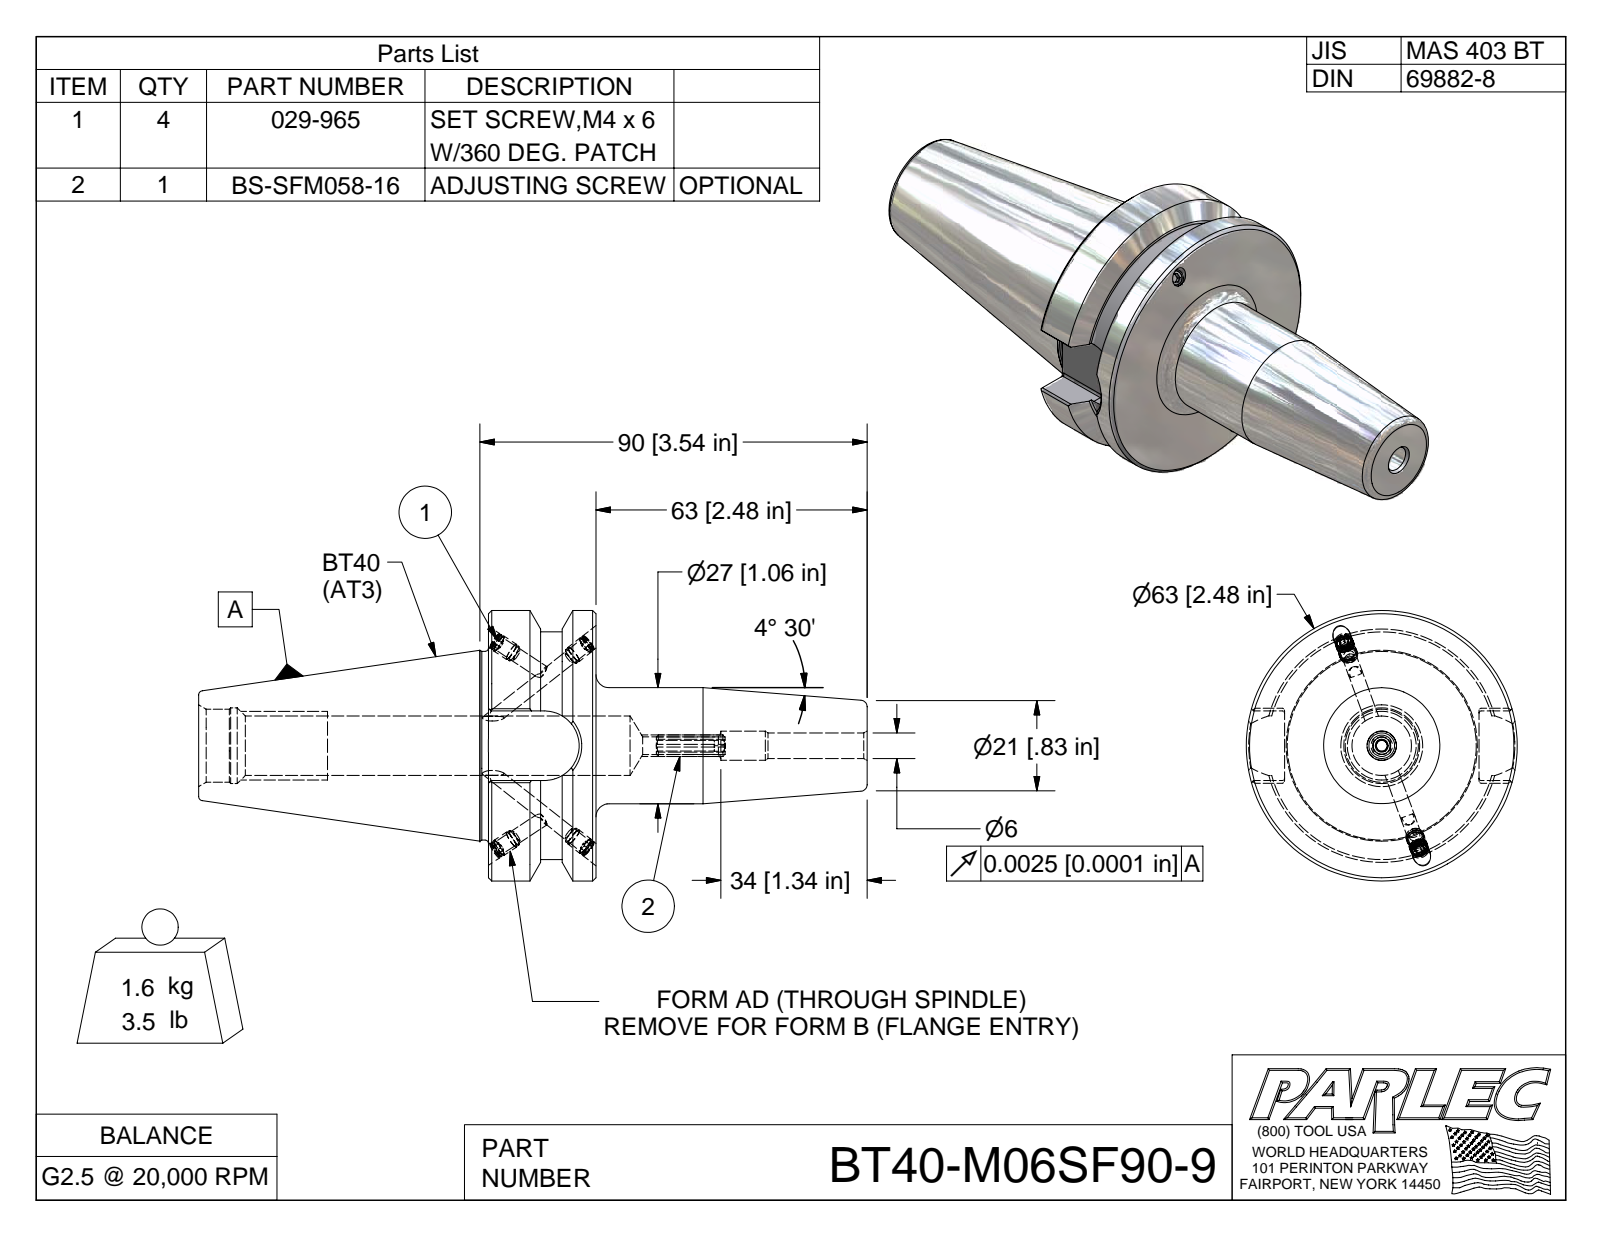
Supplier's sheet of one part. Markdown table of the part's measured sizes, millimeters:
| quantity | value |
| --- | --- |
| part name | BT40-M06SF90-9; BT40BC-M06SF90-9-1; 029-965; BS-SFM058-16 |
| STEP written by | Autodesk Inventor 2009 (AUTOMOTIVE_DESIGN) |
| units | millimeters |
| bodies | 6 solids, 173 faces (79 planar, 43 cylindrical, 51 other) |
| overall size | 155.4 × 63 × 63 |
| volume | 148 100 mm³ |
| surface area | 30 170 mm² |
| round holes (diameter × count) | 3.3 × 4, 4.1 × 4, 6 × 1, 6.8 × 1, 17.6 × 1 |
| round bosses / shafts (diameter × count) | 4.2 × 4, 4 × 4, 63 × 1, 53 × 1, 44.5 × 1, 43.9 × 1, 27 × 1 |
| partial cylindrical surfaces (radius × count) | 0.5 × 8, 2.5 × 1, 8.1 × 1 |
| main face-to-face distances | 25, 45.2, 88, 63, 67.4, 92.4, 155.4, 16.2, 20.6, 24.6 |
